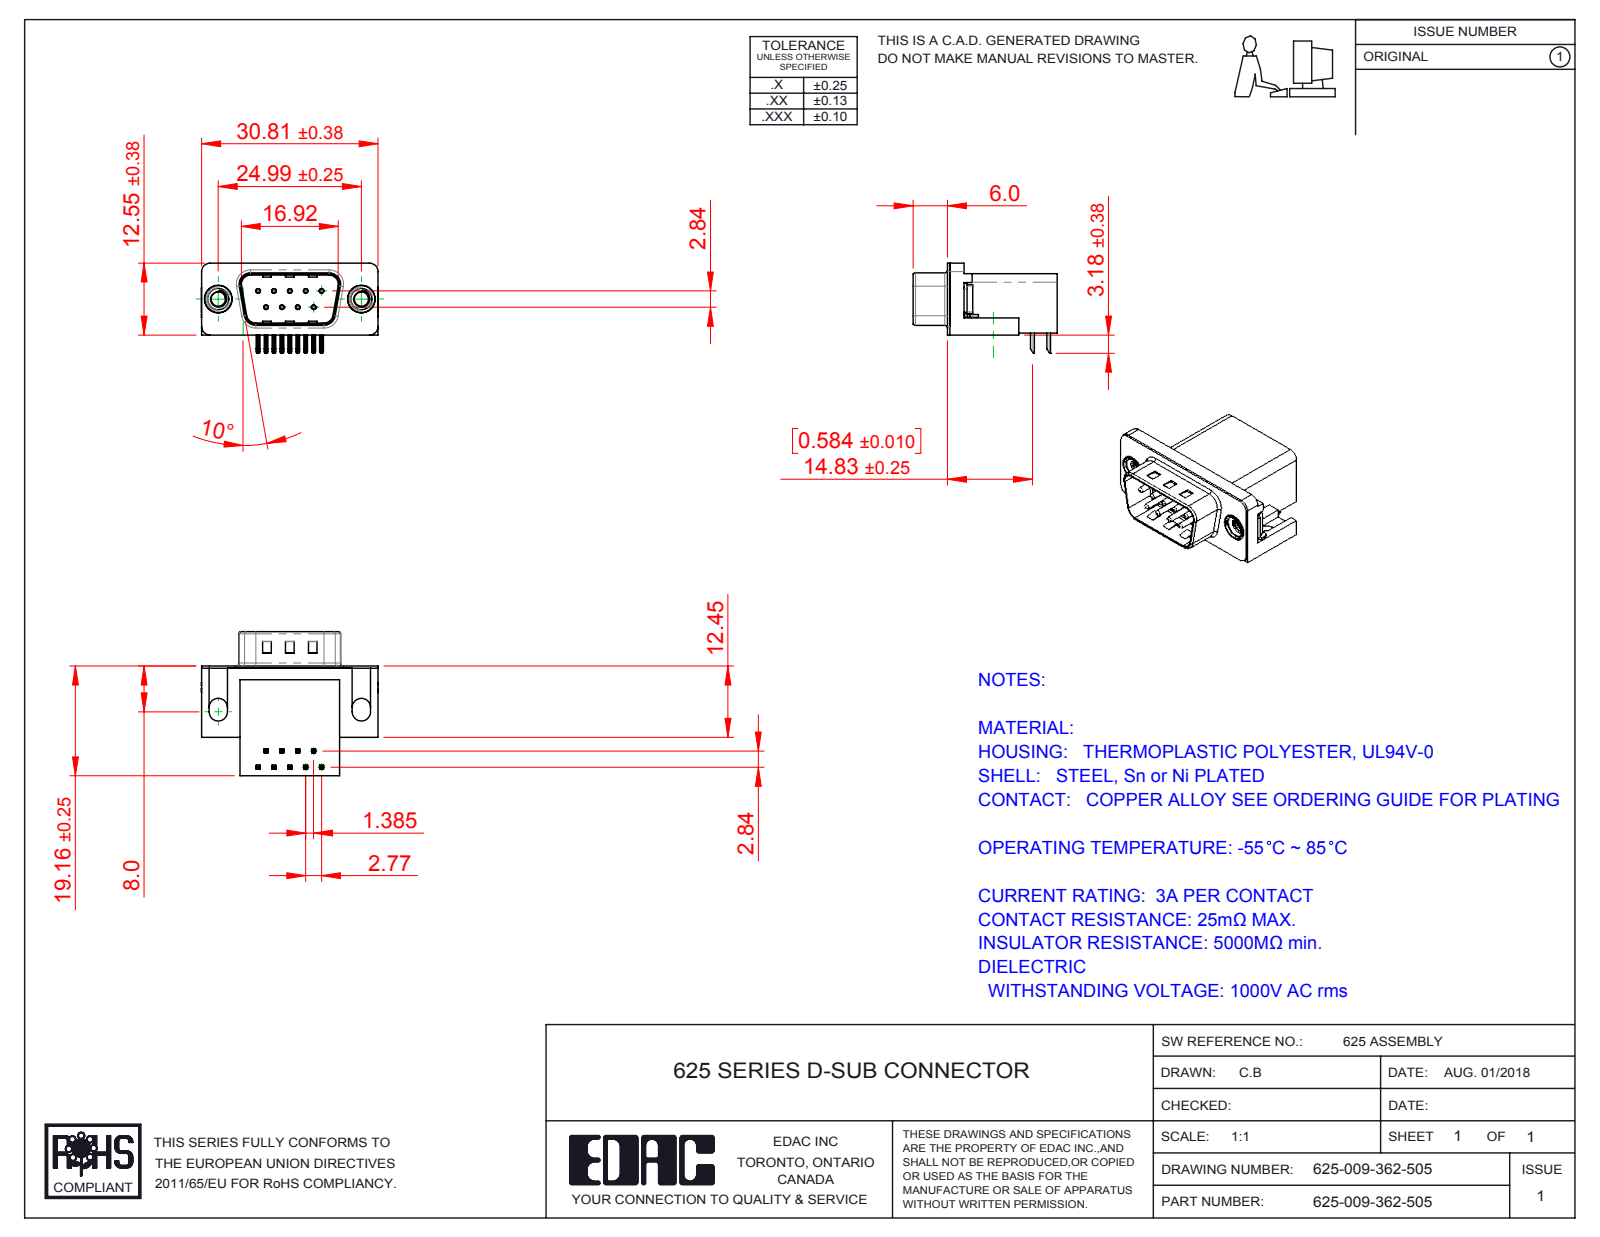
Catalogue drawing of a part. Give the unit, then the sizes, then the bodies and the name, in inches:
Units: inches
Overall size (bounding box): 1.216 × 0.991 × 0.619
Round holes (diameter × count): ⌀0.014 ×9, ⌀0.031 ×9, ⌀0.098 ×2, ⌀0.157 ×2, ⌀0.189 ×2, ⌀0.197 ×2
Round bosses / shafts (diameter × count): ⌀0.03 ×9, ⌀0.193 ×2, ⌀0.187 ×2, ⌀0.154 ×2
Partial cylindrical surfaces — rounded edges, fillets, slot ends (radius × count): R0.01 ×44, R0.005 ×18, R0.039 ×16, R0.02 ×9, R0.059 ×8, R0.063 ×8, R0.035 ×4, R0.079 ×4
Main face-to-face distances: 0.016, 0.407, 0.739, 0.754, 0.114, 0.64, 0.098, 0.014, 0.421, 0.264
Hole centre spacings: 0.124, 0.109, 0.218, 0.198, 0.198, 0.327, 0.294, 0.295
Volume: 0.271 in³ · Surface area: 7.473 in²
Bodies: 15 solids, 991 faces (575 planar, 317 cylindrical, 99 other)
Part name (STEP PRODUCT): 625-009-362-505; 625 Non Board Mount; 625 Contact Bottom; 625 M3 Threaded Rivet (+3 more)
STEP written by: SolidWorks 2016 (CONFIG_CONTROL_DESIGN)
